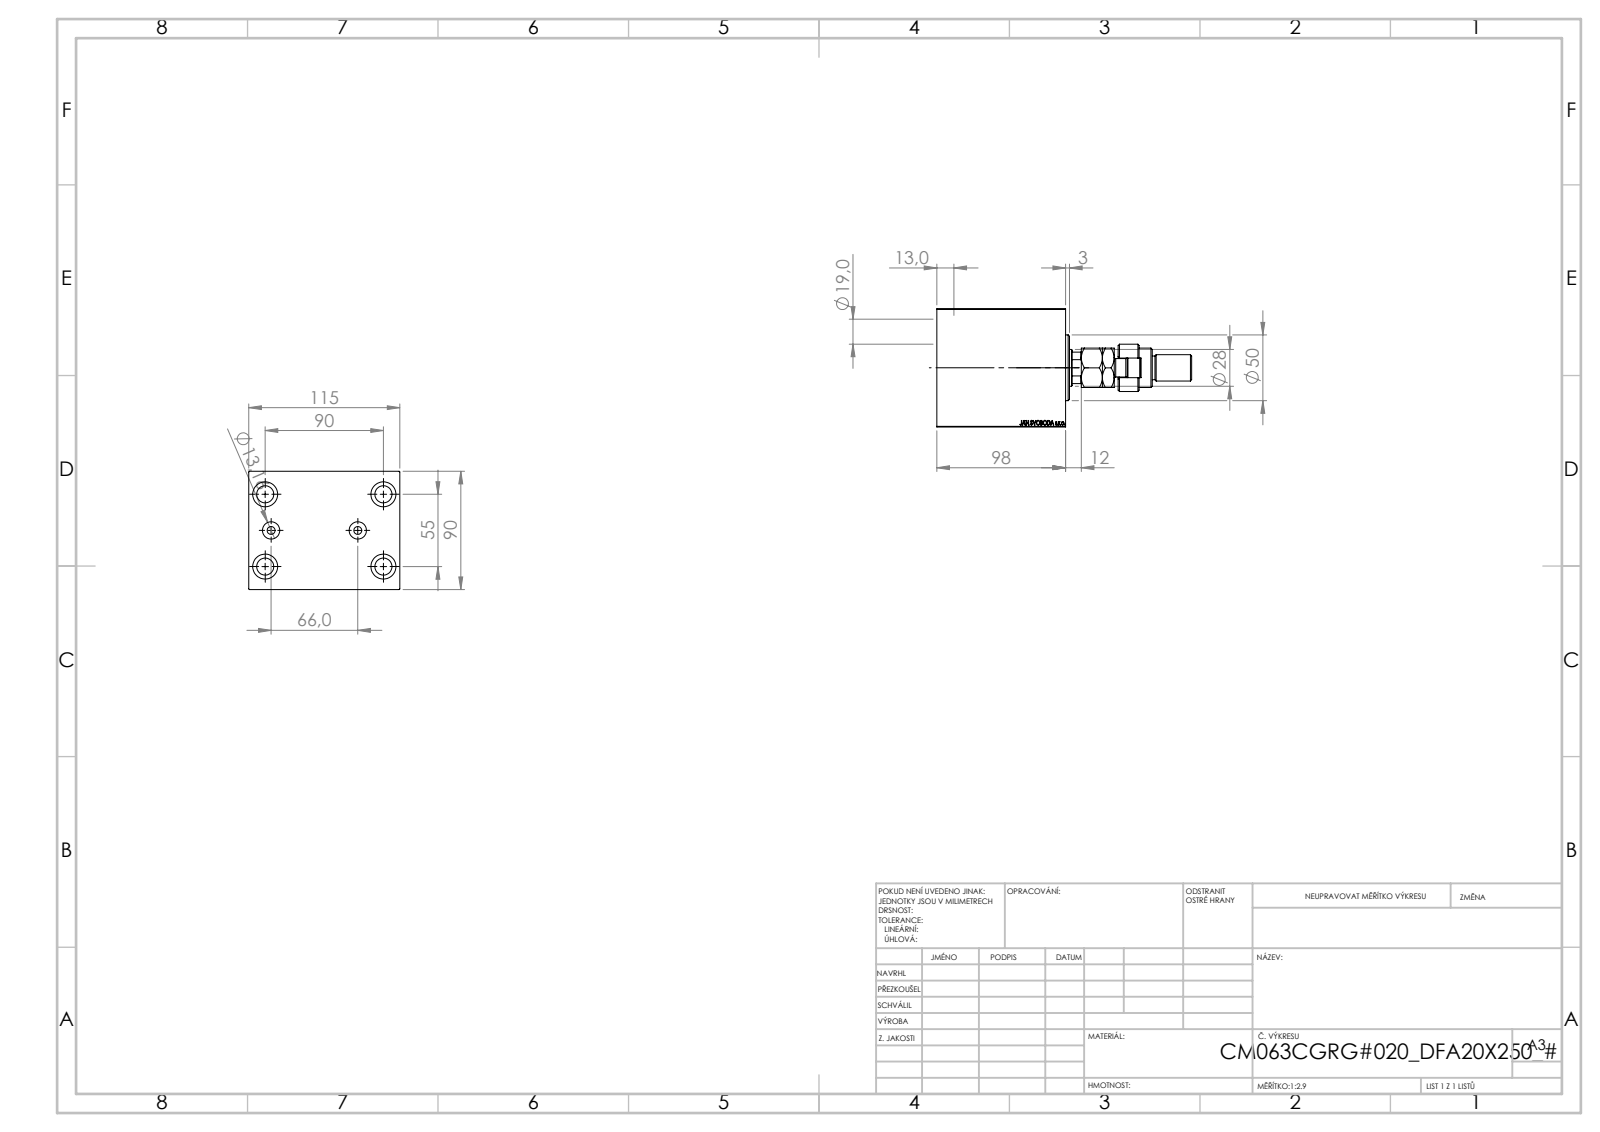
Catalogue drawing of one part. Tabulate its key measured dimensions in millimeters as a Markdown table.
| quantity | value |
| --- | --- |
| part name | MFA; V450CM_C_VCP; FEMALE_PART_FOR_DFA; V450CM_C_Body (+1 more) |
| STEP written by | SolidWorks 2019 (CONFIG_CONTROL_DESIGN) |
| units | millimeters |
| bodies | 5 solids, 946 faces (437 planar, 71 cylindrical, 438 other) |
| overall size | 195.5 × 115 × 90 |
| volume | 942 554 mm³ |
| surface area | 129 670 mm² |
| round holes (diameter × count) | 13 × 4, 19 × 4, 6 × 2, 13.16 × 2, 18.5 × 1, 28 × 1, 31.5 × 1, 63 × 1, 65 × 1, 72 × 1 |
| round bosses / shafts (diameter × count) | 50 × 1, 36 × 1, 30 × 1, 22 × 1, 20 × 1, 18 × 1, 14 × 1 |
| partial cylindrical surfaces (radius × count) | 7.5 × 1, 12 × 1, 13.5 × 1 |
| main face-to-face distances | 90, 115, 98, 48.5, 49.5, 30, 88, 10, 5, 39.5 |
| hole center spacings | 30, 52.74, 82.71, 33, 55, 90, 105.48, 66 |
